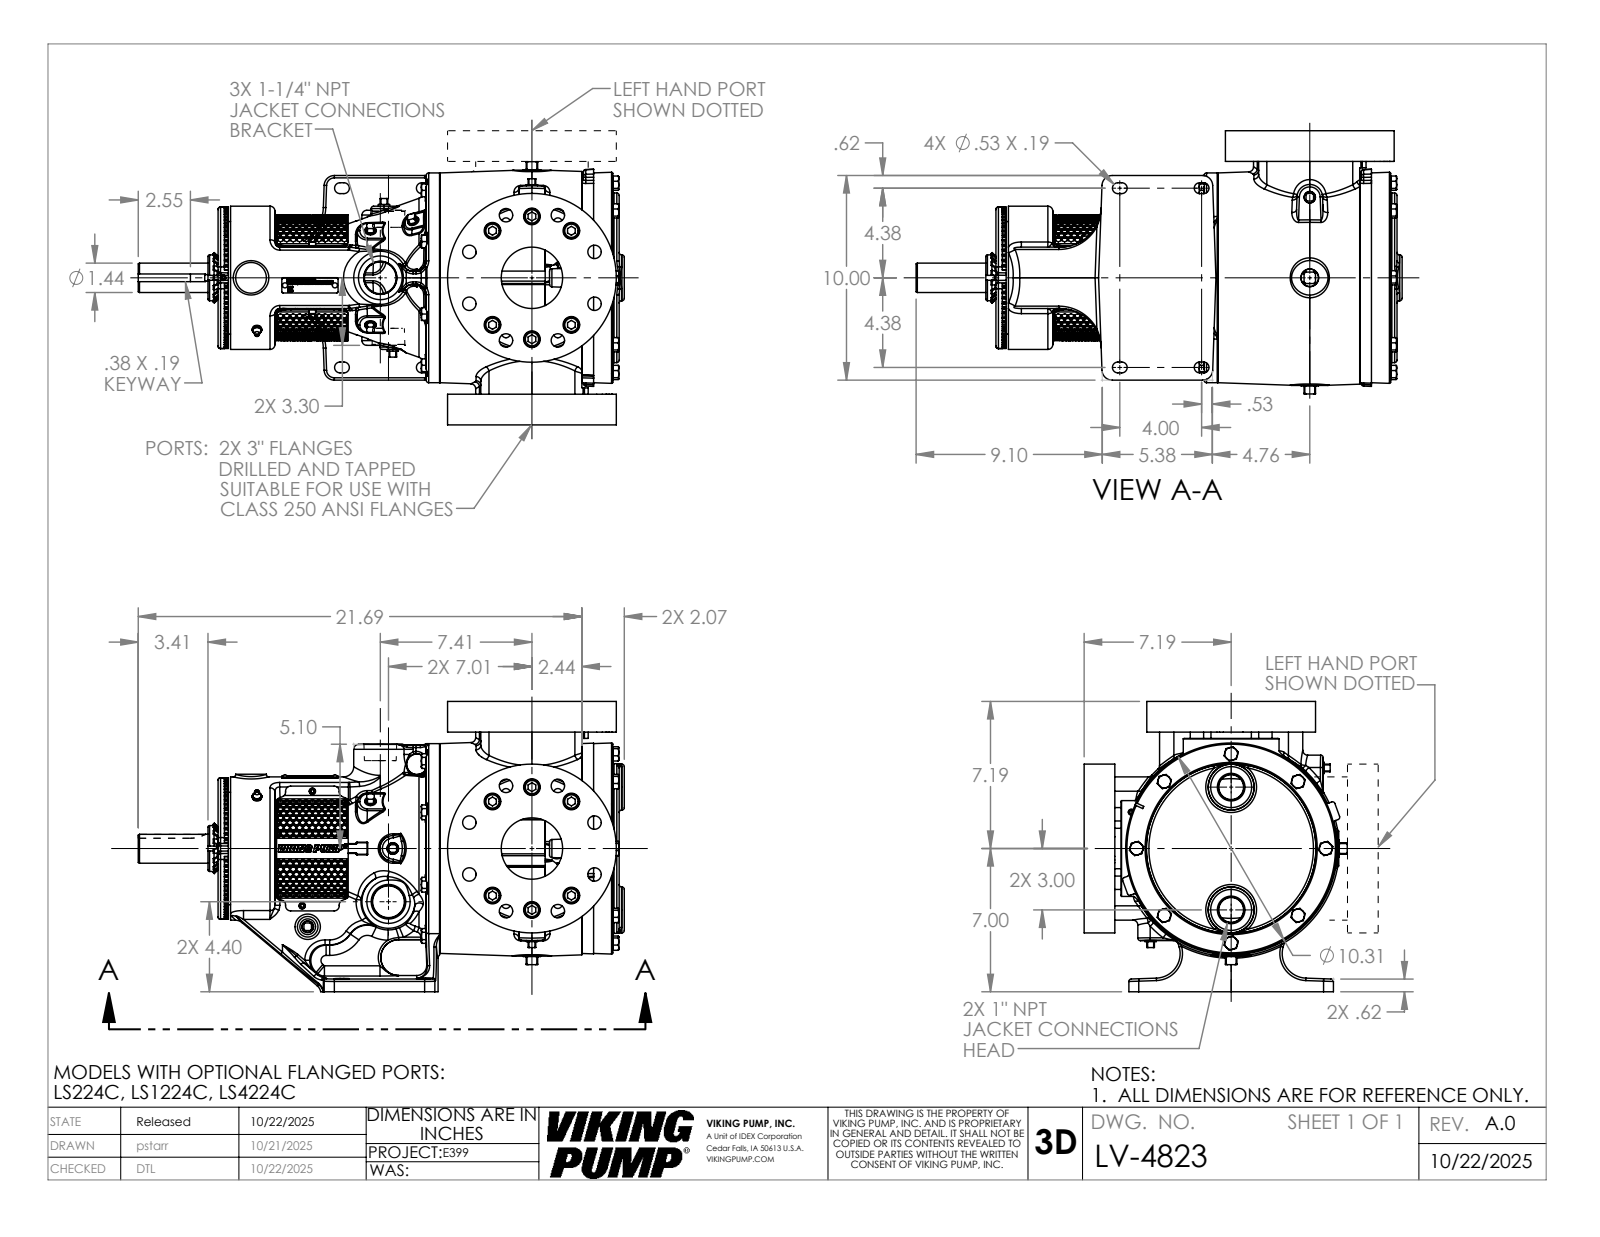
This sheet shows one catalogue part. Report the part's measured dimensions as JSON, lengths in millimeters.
{"part_name": "LV-4823", "step_written_by": "SolidWorks 2024 (AUTOMOTIVE_DESIGN)", "units": "millimeters", "bodies": {"solids": 1, "faces": 4484, "planar": 1511, "cylindrical": 870, "other": 2103}, "overall_size": [603.5, 360.4, 326.7], "volume_mm3": 21830000, "surface_area_mm2": 989700, "round_holes": [[16.7, 16], [20.6, 12], [6.4, 9], [27.8, 8], [5.1, 6], [4, 3], [6.8, 2], [8, 2], [76.2, 2], [11.5, 1], [38.3, 1], [40.1, 1]], "round_bosses_or_shafts": [[19.1, 12], [15.9, 9], [15.9, 7], [7.9, 3], [4.8, 3], [209.6, 2], [260.4, 1], [177.8, 1]], "partial_cylinders_radius": [[1.6, 109], [1.8, 74], [3, 66], [12.7, 26], [0.8, 18], [6.1, 16], [25.4, 16], [6.4, 12]], "face_to_face_distances": [38.1, 360.3, 7.9, 322.2, 57.2, 330.4, 338.3, 12.7, 89.9, 420.3], "hole_center_spacings": [76.2, 84.2, 119, 155.4, 34.9, 25.6, 32.2, 38.9]}
